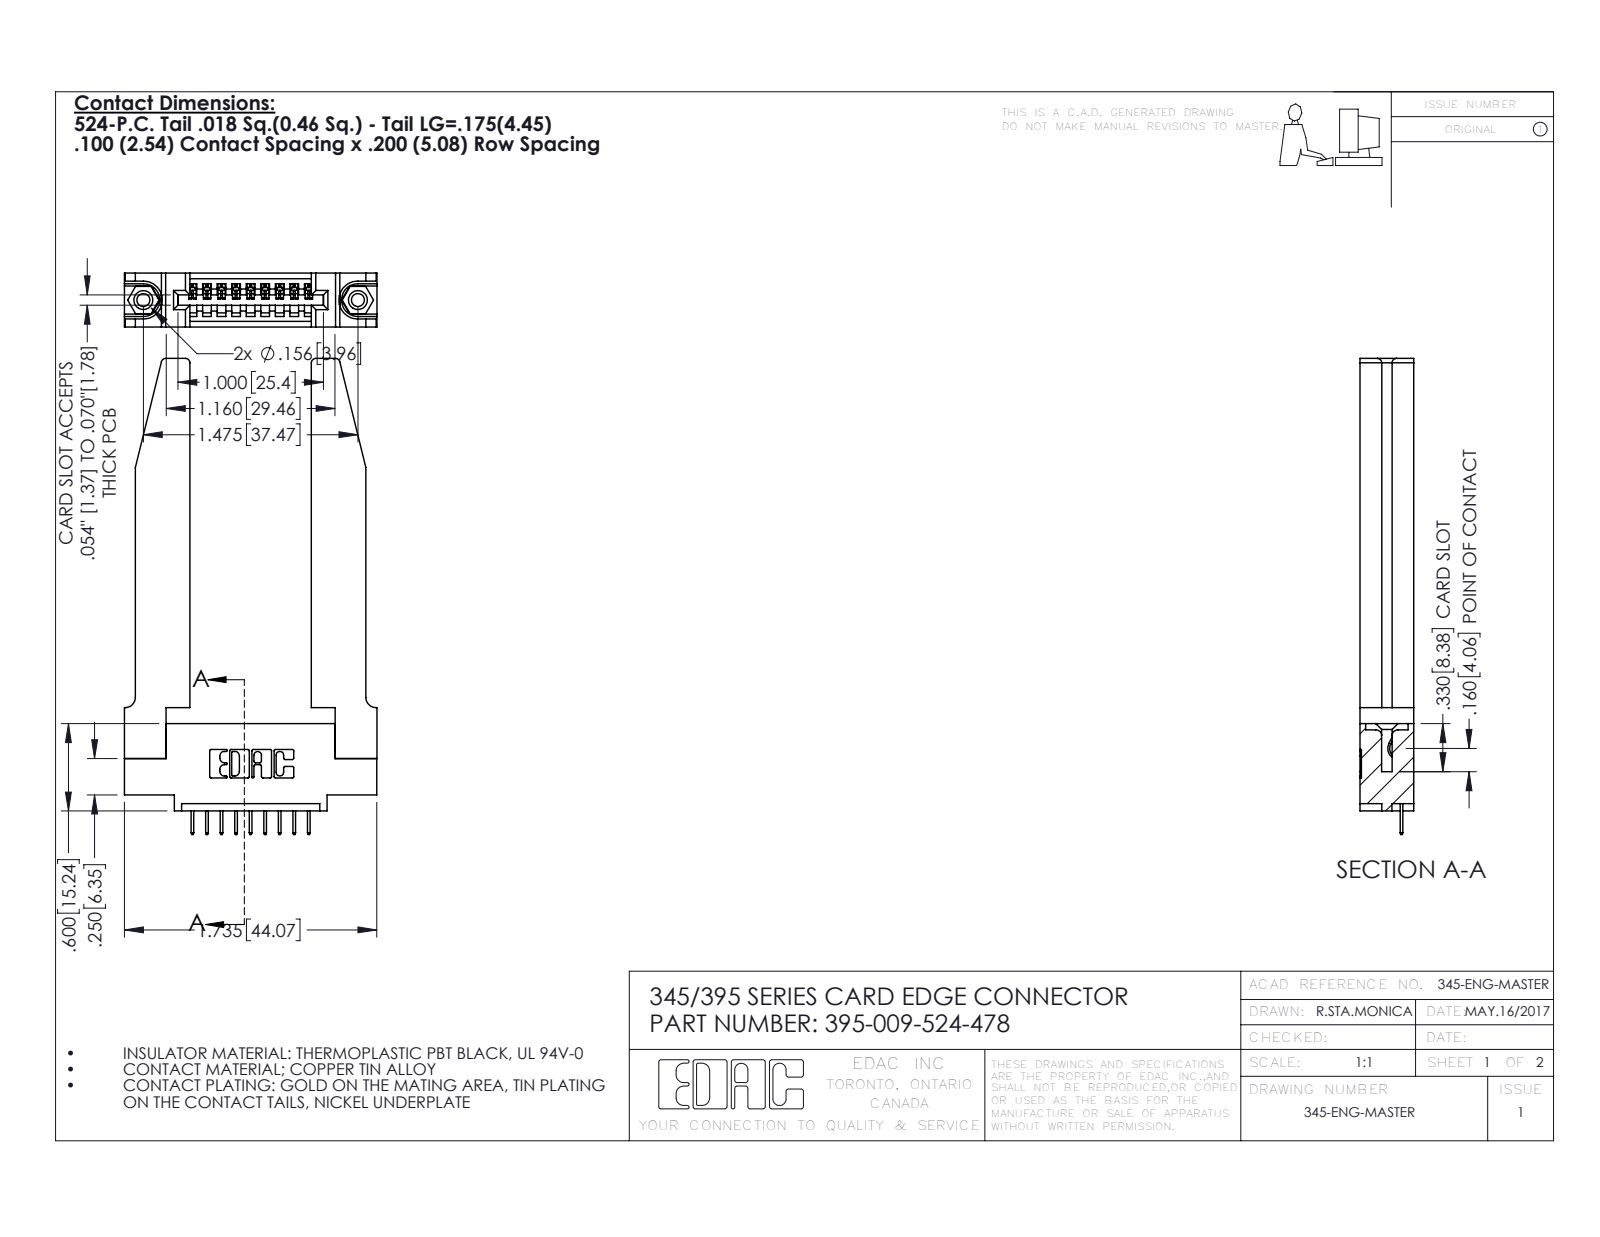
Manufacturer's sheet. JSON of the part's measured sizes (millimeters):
{"part_name": "345-292-001_345-293-124; 395-009-524-478; 345 Part_0.110 Offset - 0.156 Dia-TH; 345-250-001_345-250-001-102 (+1 more)", "step_written_by": "SolidWorks 2016 (CONFIG_CONTROL_DESIGN)", "units": "millimeters", "bodies": {"solids": 14, "faces": 922, "planar": 640, "cylindrical": 230, "other": 52}, "overall_size": [83.1, 44.1, 9.4], "volume_mm3": 11600, "surface_area_mm2": 11430, "round_holes": [[2.3, 2], [3.2, 2], [4, 2], [1.6, 1]], "round_bosses_or_shafts": [[3.9, 2]], "partial_cylinders_radius": [[0.3, 22], [0.2, 18], [0.8, 8], [0.2, 6], [0.8, 6], [0.7, 3], [0.8, 2], [1, 2]], "face_to_face_distances": [9.4, 3.8, 1.8, 3.8, 5.6, 7.6, 2, 21.2, 1.8, 1.4], "hole_center_spacings": [6.9, 31.6, 37.5]}
